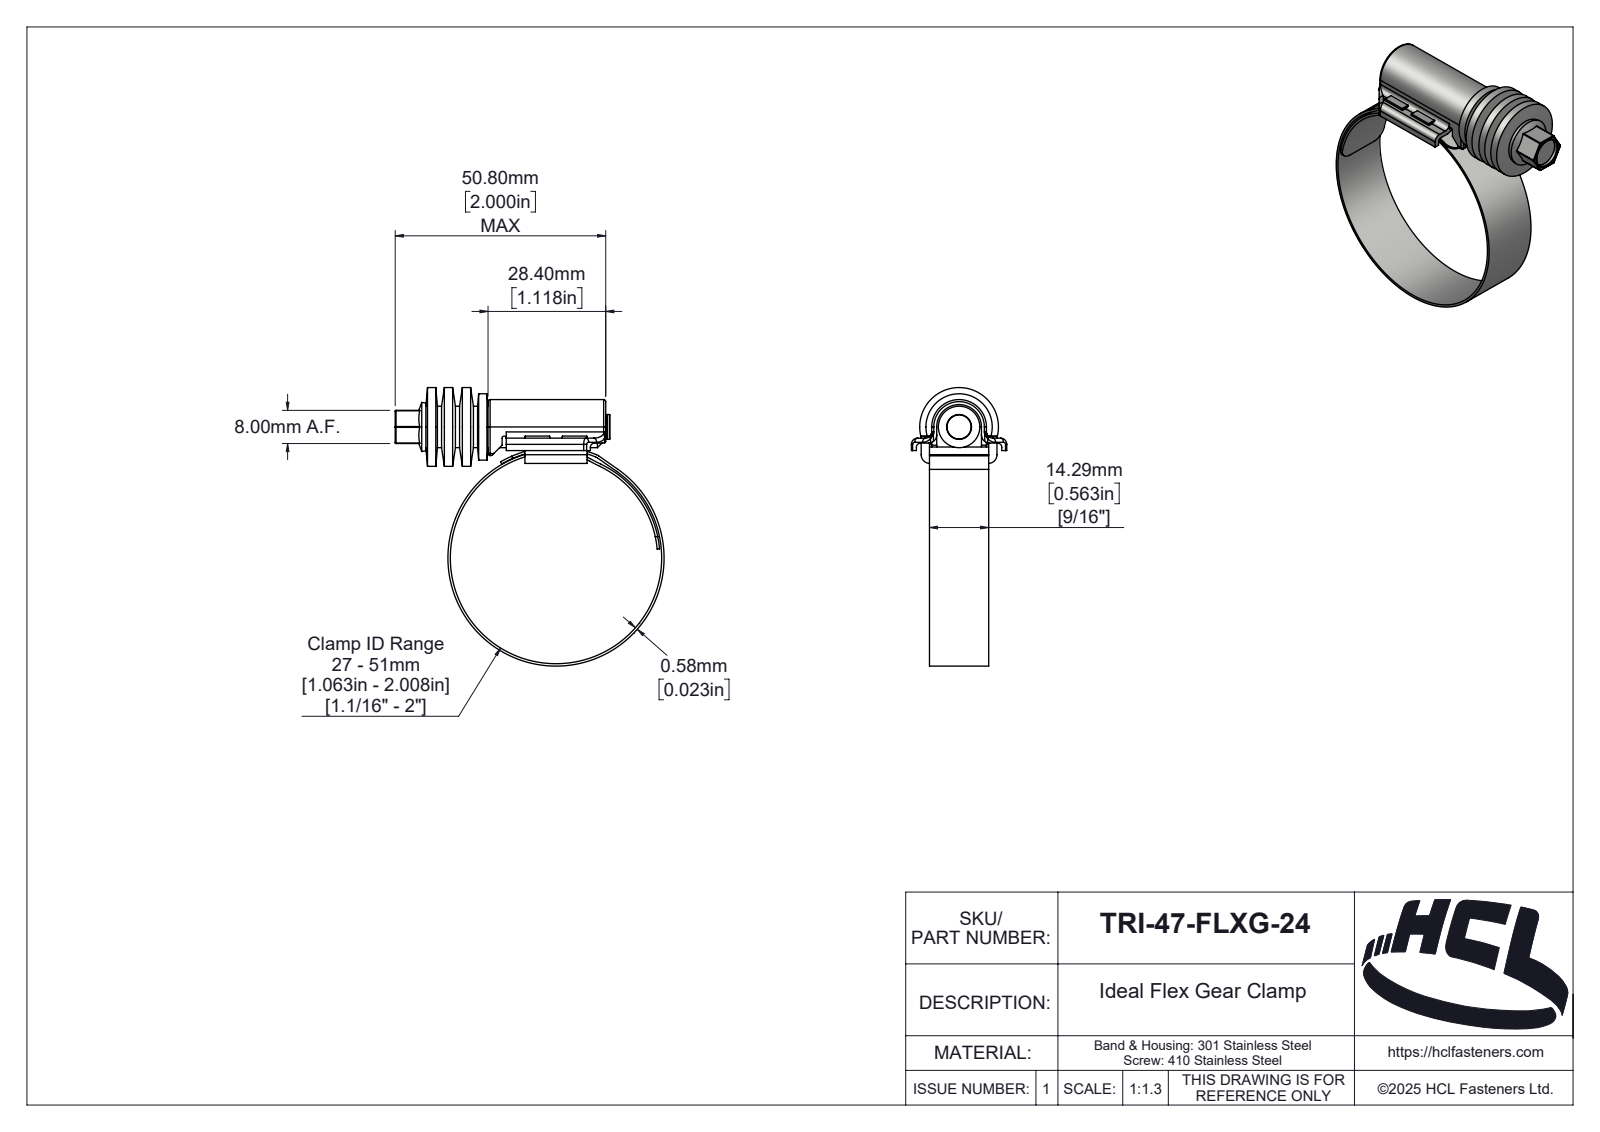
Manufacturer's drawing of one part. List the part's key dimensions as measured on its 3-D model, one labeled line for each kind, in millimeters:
Part name (STEP PRODUCT): TRI-47-FLXG-24
STEP written by: SolidWorks 2025 (AUTOMOTIVE_DESIGN)
Units: millimetres
Bodies: 4 solids, 323 faces (88 planar, 139 cylindrical, 96 other)
Overall size (bounding box): 67.18 × 64.88 × 23
Volume: 9 346 mm³ · Surface area: 12 792 mm²
Round holes (diameter × count): ⌀7 ×1, ⌀51 ×1
Round bosses / shafts (diameter × count): ⌀52.16 ×1, ⌀19 ×1, ⌀16 ×1, ⌀10 ×1, ⌀6 ×1, ⌀5 ×1
Partial cylindrical surfaces — rounded edges, fillets, slot ends (radius × count): R0.2 ×12, R0.5 ×9, R1 ×8, R1.5 ×4, R3 ×4, R2 ×3, R0.1 ×2, R2.1 ×2
Main face-to-face distances: 2, 1.2, 4.9, 14.28, 1.74, 12.54, 16.29, 6.1, 0.54, 13.74
